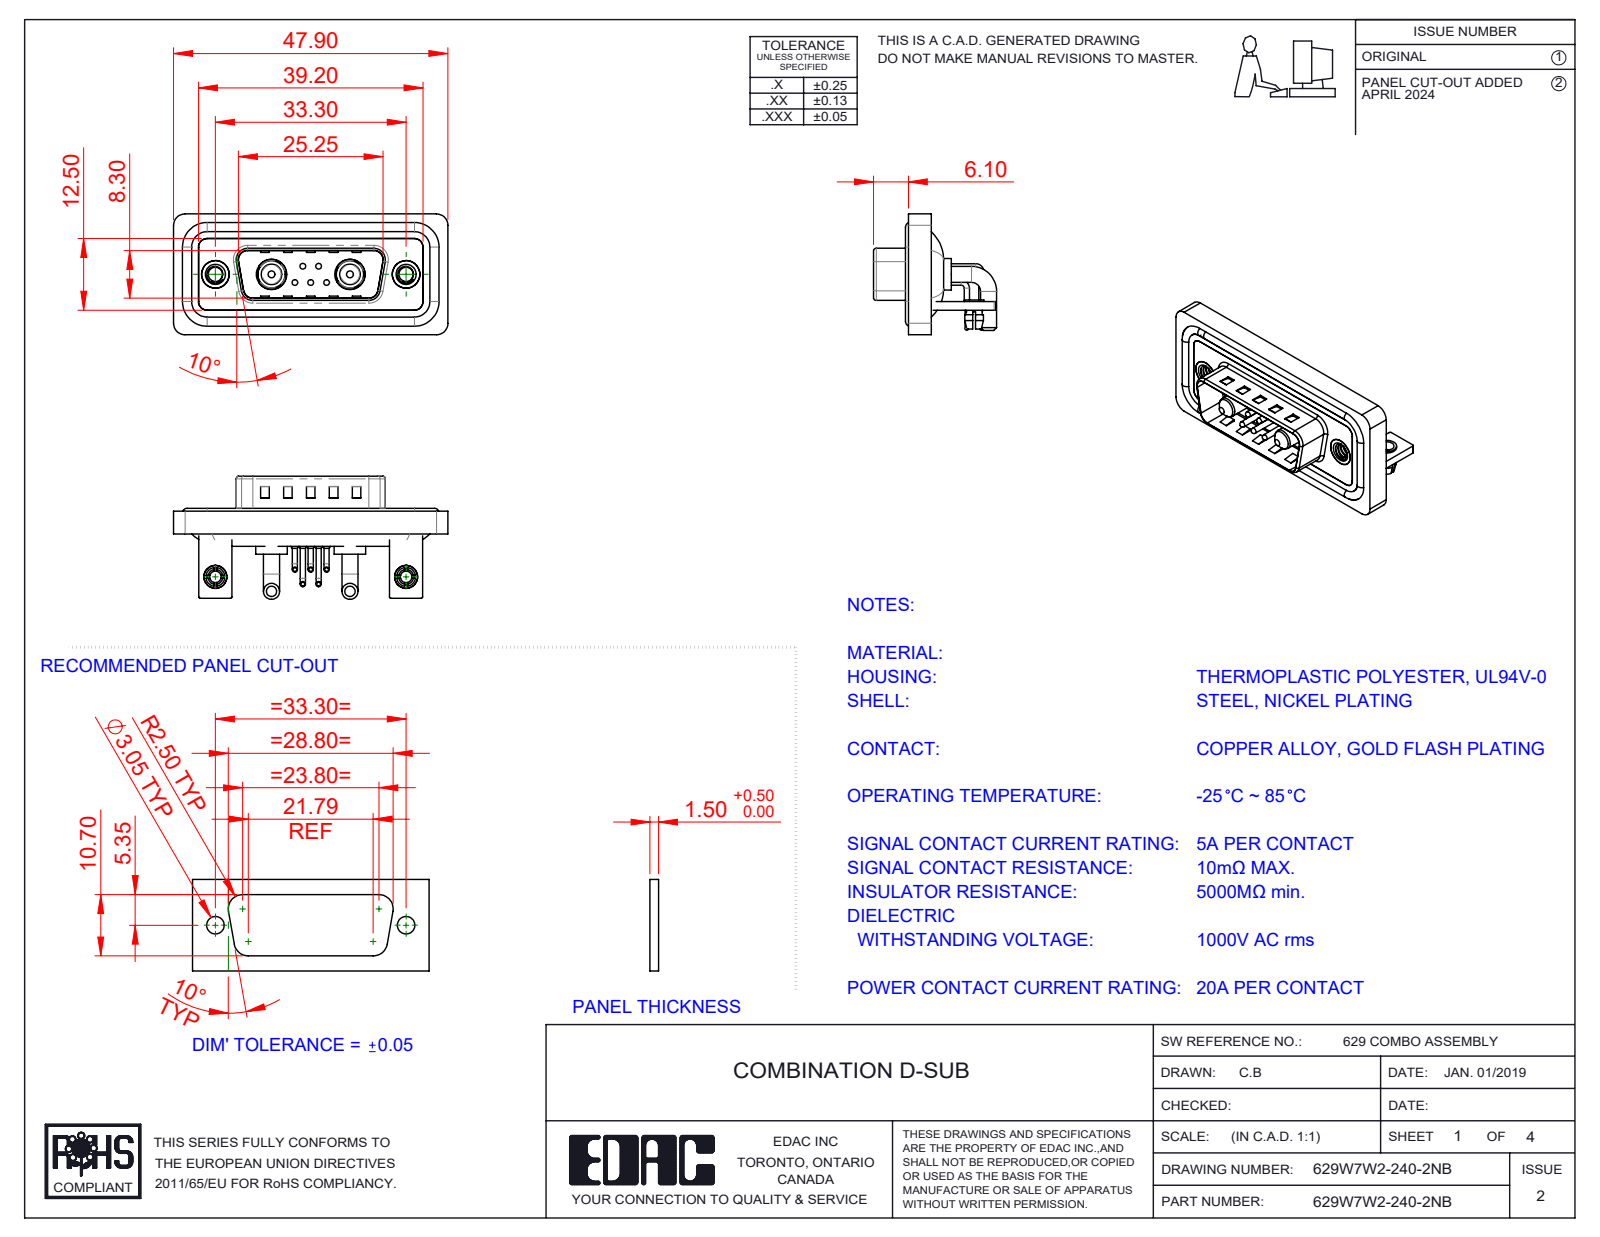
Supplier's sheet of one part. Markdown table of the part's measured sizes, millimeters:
| quantity | value |
| --- | --- |
| part name | 629Combo Shell Rear_15 Contacts; 629Combo Threaded Rivet_B; 629Combo Contact Row 2; 629Combo Board Lock (+7 more) |
| STEP written by | SolidWorks 2023 (CONFIG_CONTROL_DESIGN) |
| units | millimeters |
| bodies | 20 solids, 1213 faces (585 planar, 456 cylindrical, 172 other) |
| overall size | 47.9 × 21.5 × 21.1 |
| volume | 5 989 mm³ |
| surface area | 9 939 mm² |
| round holes (diameter × count) | 2 × 7, 0.75 × 5, 1.6 × 5, 2.5 × 4, 3.2 × 2, 4 × 2, 4.8 × 2, 4.85 × 2, 5 × 2, 5.3 × 2 |
| round bosses / shafts (diameter × count) | 0.9 × 10, 1.5 × 5, 1 × 5, 0.65 × 5, 2.8 × 4, 1.6 × 4, 5.5 × 2, 5.2 × 2 |
| partial cylindrical surfaces (radius × count) | 2 × 21, 1.5 × 18, 0.25 × 16, 0.5 × 9, 1.6 × 8, 1.01 × 5, 0.6 × 4, 0.65 × 4 |
| main face-to-face distances | 0.4, 1.5, 0.8, 2.9, 2.1, 1.1, 1.6, 1.2, 3.7, 4.5 |
| hole center spacings | 3.16, 2.77, 9.8, 23.5, 33.3, 4.31, 4.33, 5.03 |
